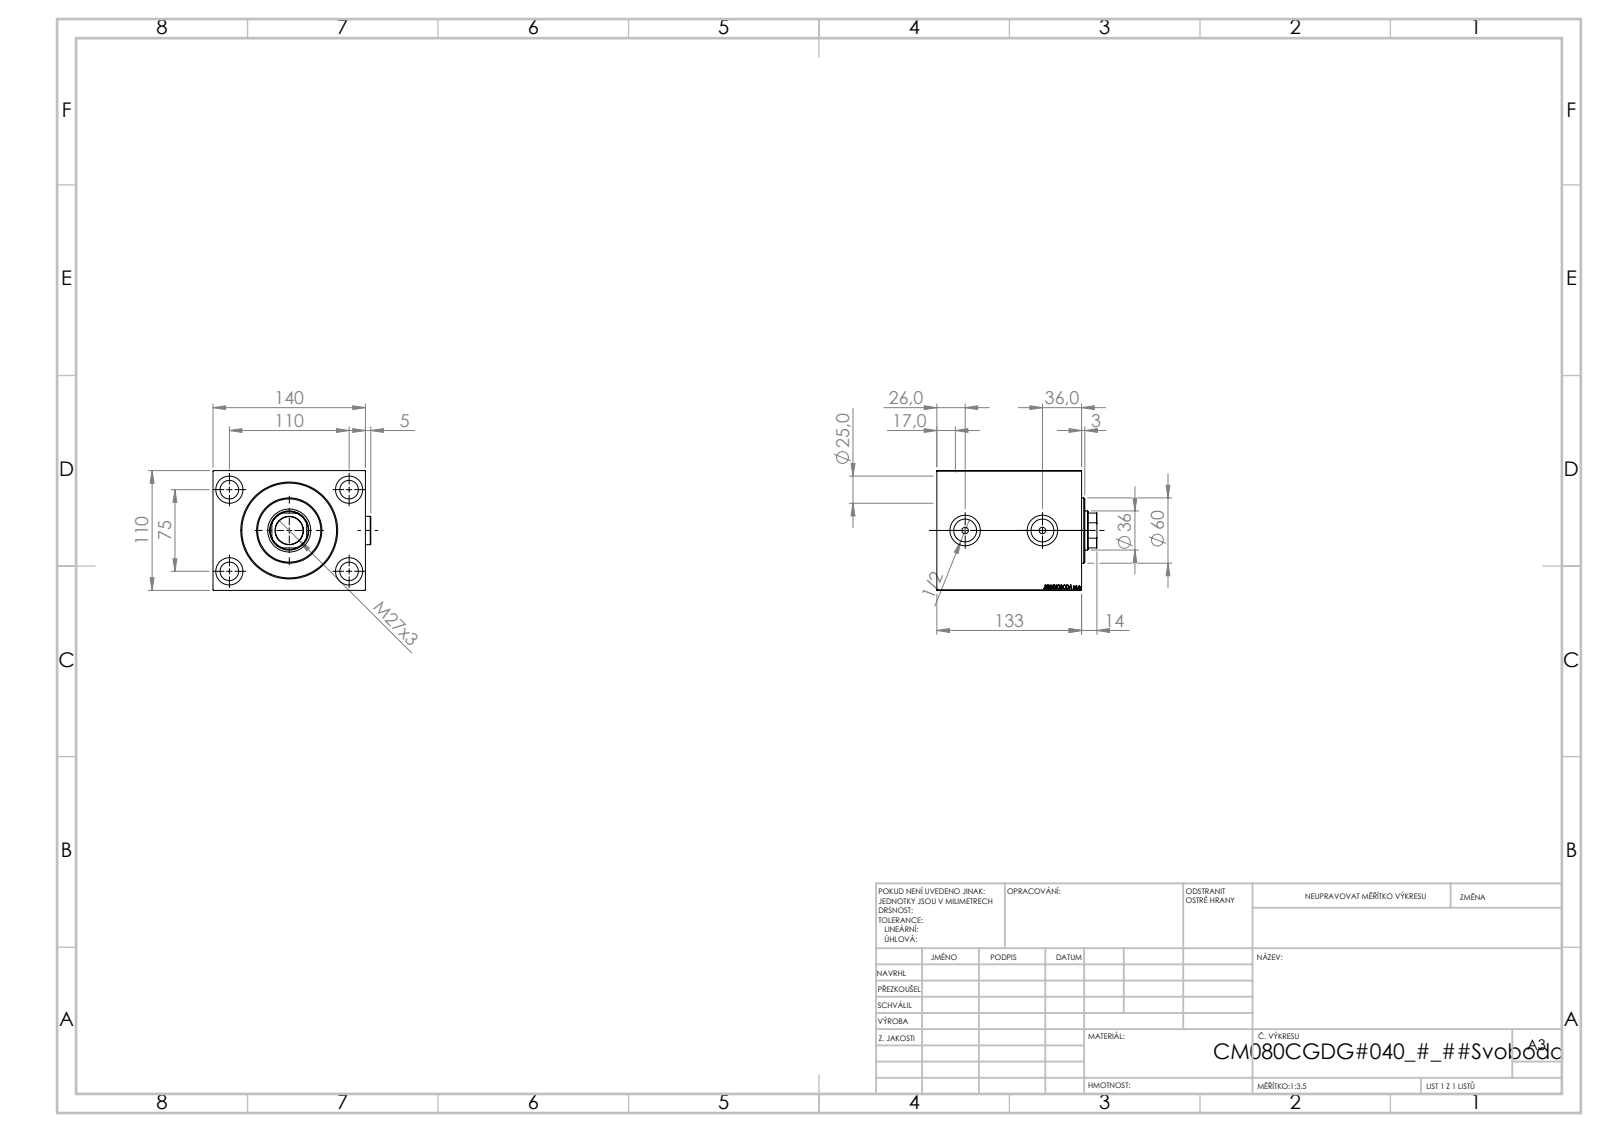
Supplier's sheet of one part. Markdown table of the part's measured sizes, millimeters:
| quantity | value |
| --- | --- |
| part name | V450CM_C_VCP; V450CM_C_Body; Zatka_OIL_PORT; V450CM_VC_B |
| STEP written by | SolidWorks 2019 (CONFIG_CONTROL_DESIGN) |
| units | millimeters |
| bodies | 5 solids, 919 faces (443 planar, 78 cylindrical, 398 other) |
| overall size | 147 × 144.9 × 110 |
| volume | 1 716 000 mm³ |
| surface area | 213 843 mm² |
| round holes (diameter × count) | 17 × 4, 25 × 4, 6 × 2, 20.96 × 2, 28 × 2, 25.5 × 1, 36 × 1, 39.5 × 1, 80 × 1, 82 × 1, 87 × 1 |
| round bosses / shafts (diameter × count) | 26 × 2, 60 × 1 |
| partial cylindrical surfaces (radius × count) | 17.5 × 1 |
| main face-to-face distances | 110, 140, 133, 112, 21, 119, 14, 98, 54, 40 |
| hole center spacings | 66.57, 75, 110, 133.14, 71 |
